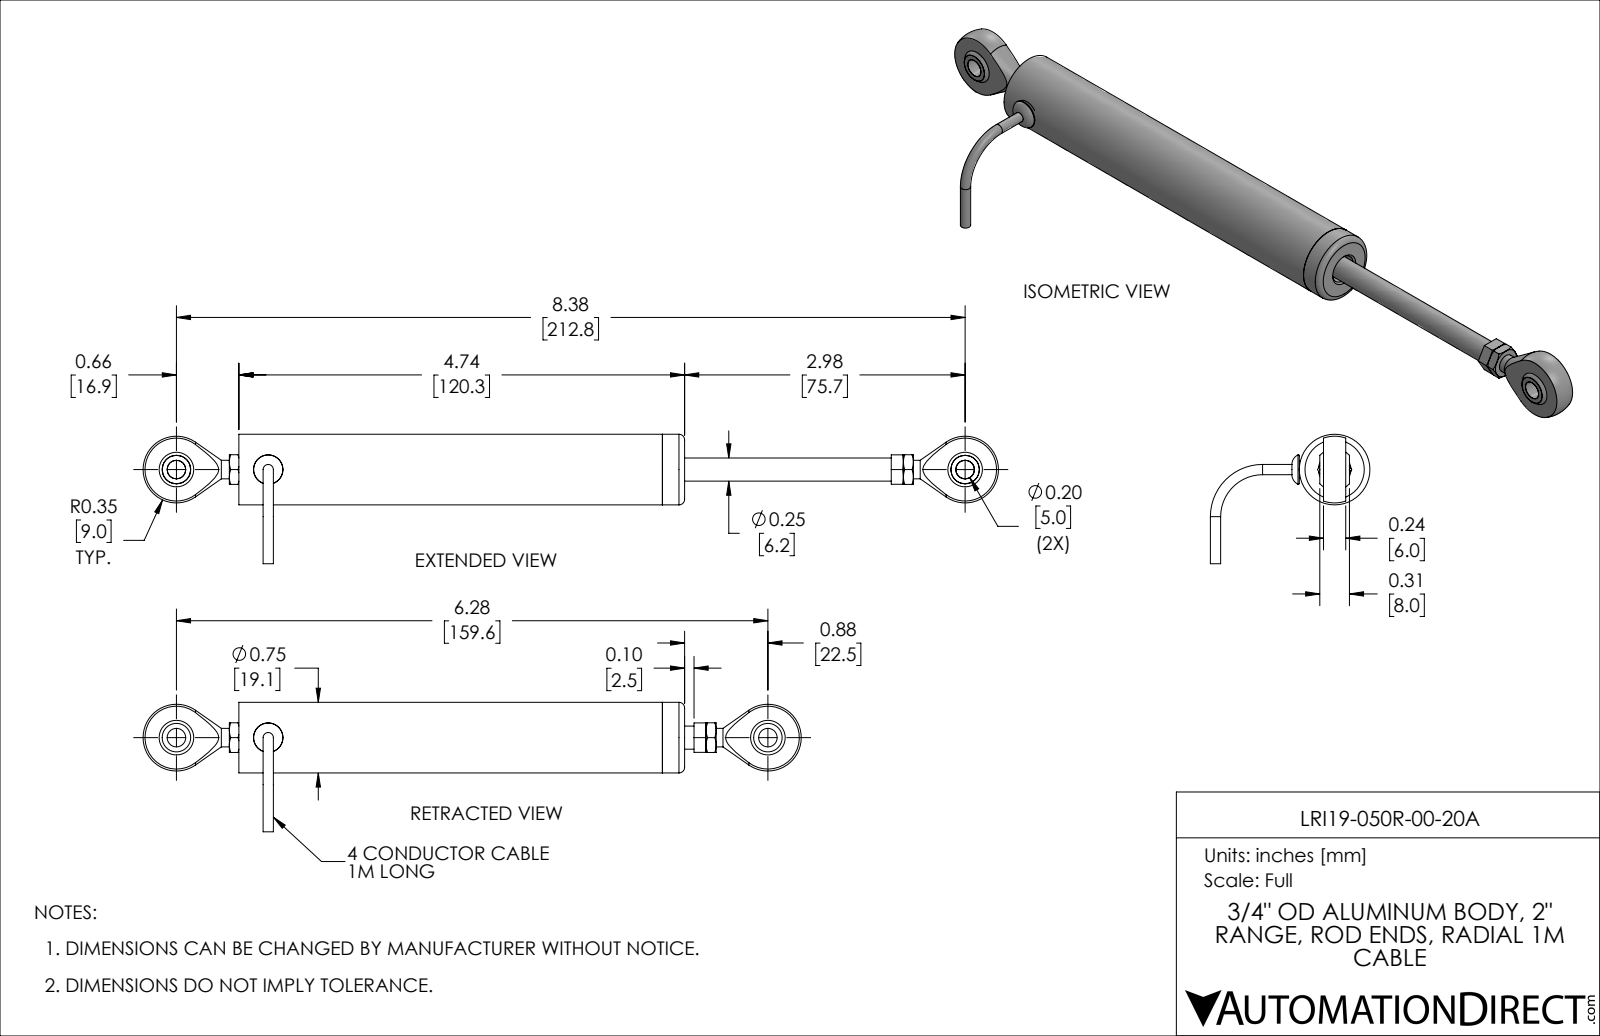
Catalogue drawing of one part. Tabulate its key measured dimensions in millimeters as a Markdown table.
| quantity | value |
| --- | --- |
| part name | LRI19-050R-00-20A |
| STEP written by | SolidWorks 2019 (AUTOMOTIVE_DESIGN) |
| units | millimeters |
| bodies | 12 solids, 154 faces (58 planar, 34 cylindrical, 62 other) |
| overall size | 176.6 × 43.1 × 34.9 |
| volume | 16 930 mm³ |
| surface area | 23 360 mm² |
| round holes (diameter × count) | 5 × 2, 2.8 × 1, 4.2 × 1, 4.8 × 1, 4.9 × 1, 5.6 × 1, 7.8 × 1, 15.7 × 1, 15.9 × 1, 16.5 × 1, 18 × 1, 18.4 × 1 |
| round bosses / shafts (diameter × count) | 19.1 × 1, 17.8 × 1, 15.8 × 1, 6.2 × 1, 5.7 × 1, 5.5 × 1, 5 × 1, 2.8 × 1 |
| main face-to-face distances | 6, 2.7, 117.5, 120.2, 114.2, 111.5, 6, 8, 1, 7 |
| hole center spacings | 134.8 |
